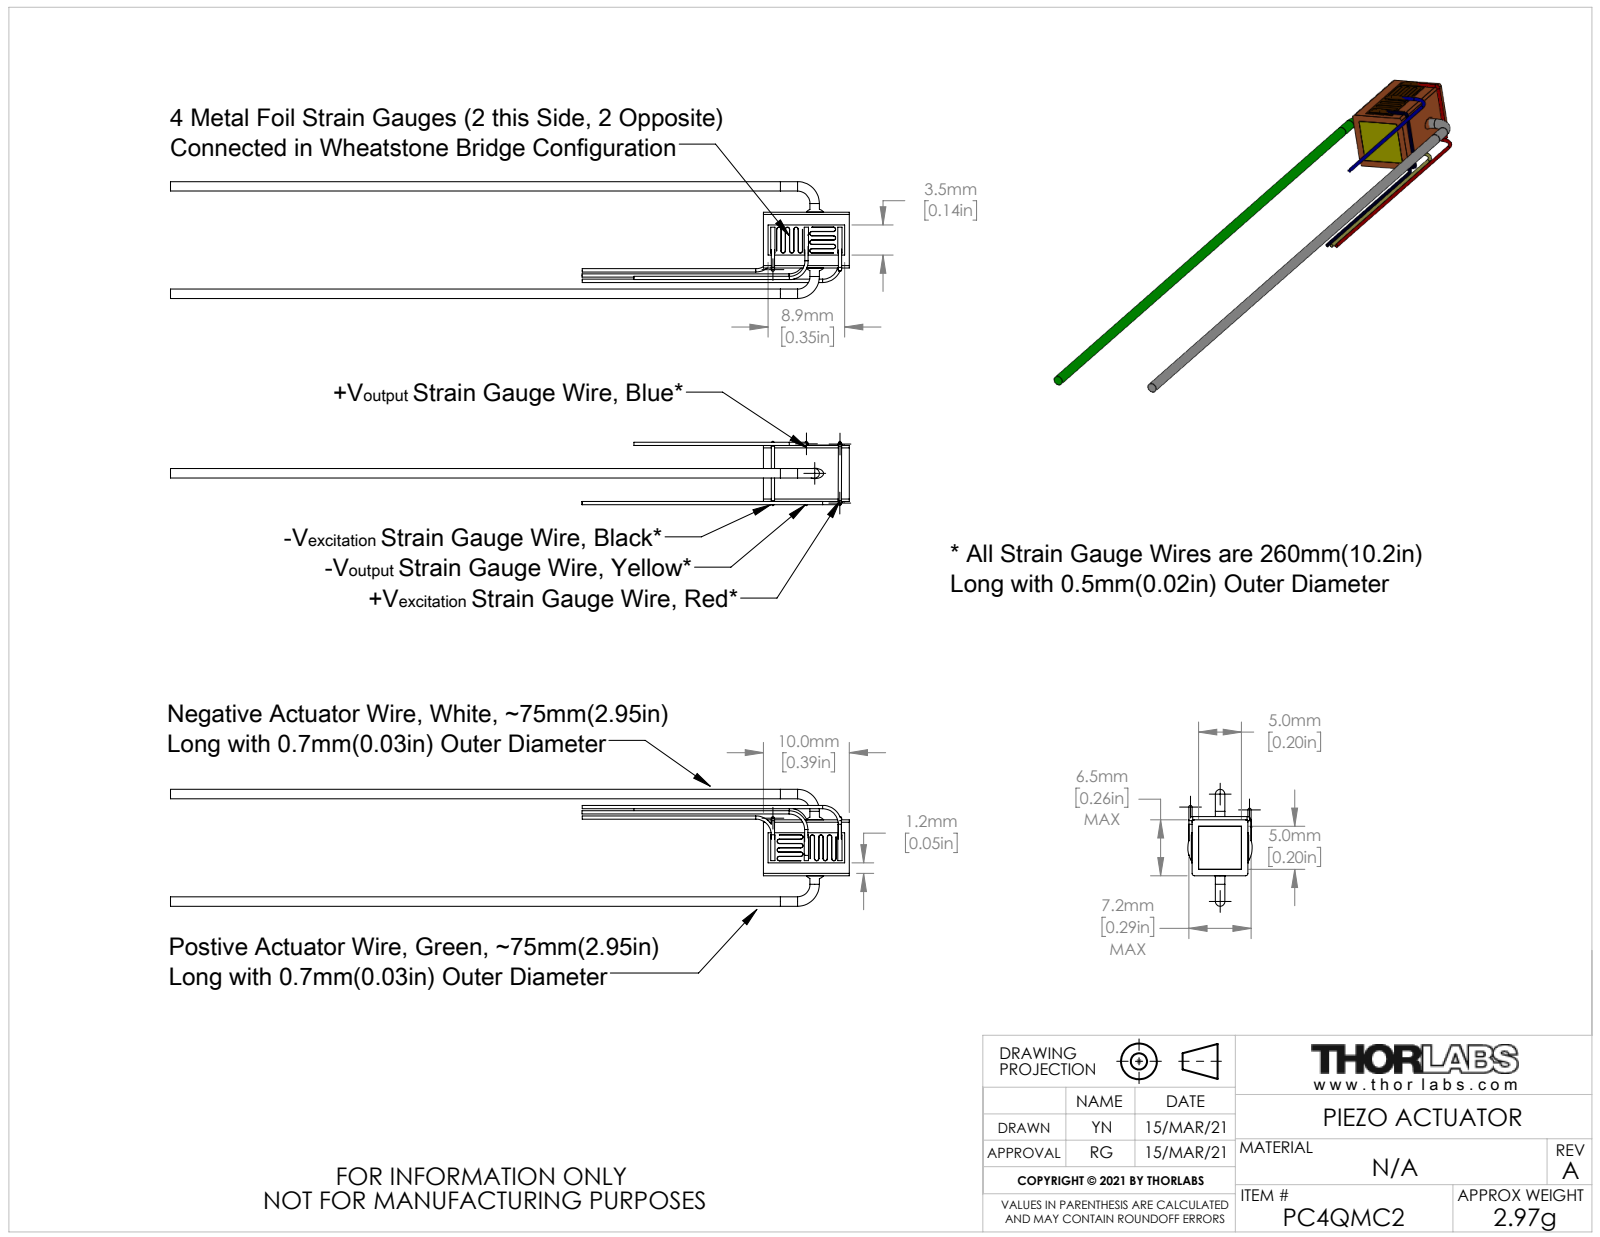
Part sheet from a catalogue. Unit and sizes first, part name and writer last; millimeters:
Units: millimetres
Overall size (bounding box): 79.03 × 13.6 × 7.5
Round bosses / shafts (diameter × count): ⌀0.38 ×12, ⌀1.1 ×3
Partial cylindrical surfaces — rounded edges, fillets, slot ends (radius × count): R0.24 ×24, R0.26 ×24, R0.27 ×4
Main face-to-face distances: 0.75, 5.75, 5, 6.5, 0.8, 5.8, 6.55, 10, 6.6, 0.5
Volume: 590 mm³ · Surface area: 1 587 mm²
Bodies: 12 solids, 268 faces (132 planar, 104 cylindrical, 32 other)
Part name (STEP PRODUCT): CTN017168-E0W
STEP written by: SolidWorks 2018 (AUTOMOTIVE_DESIGN)
